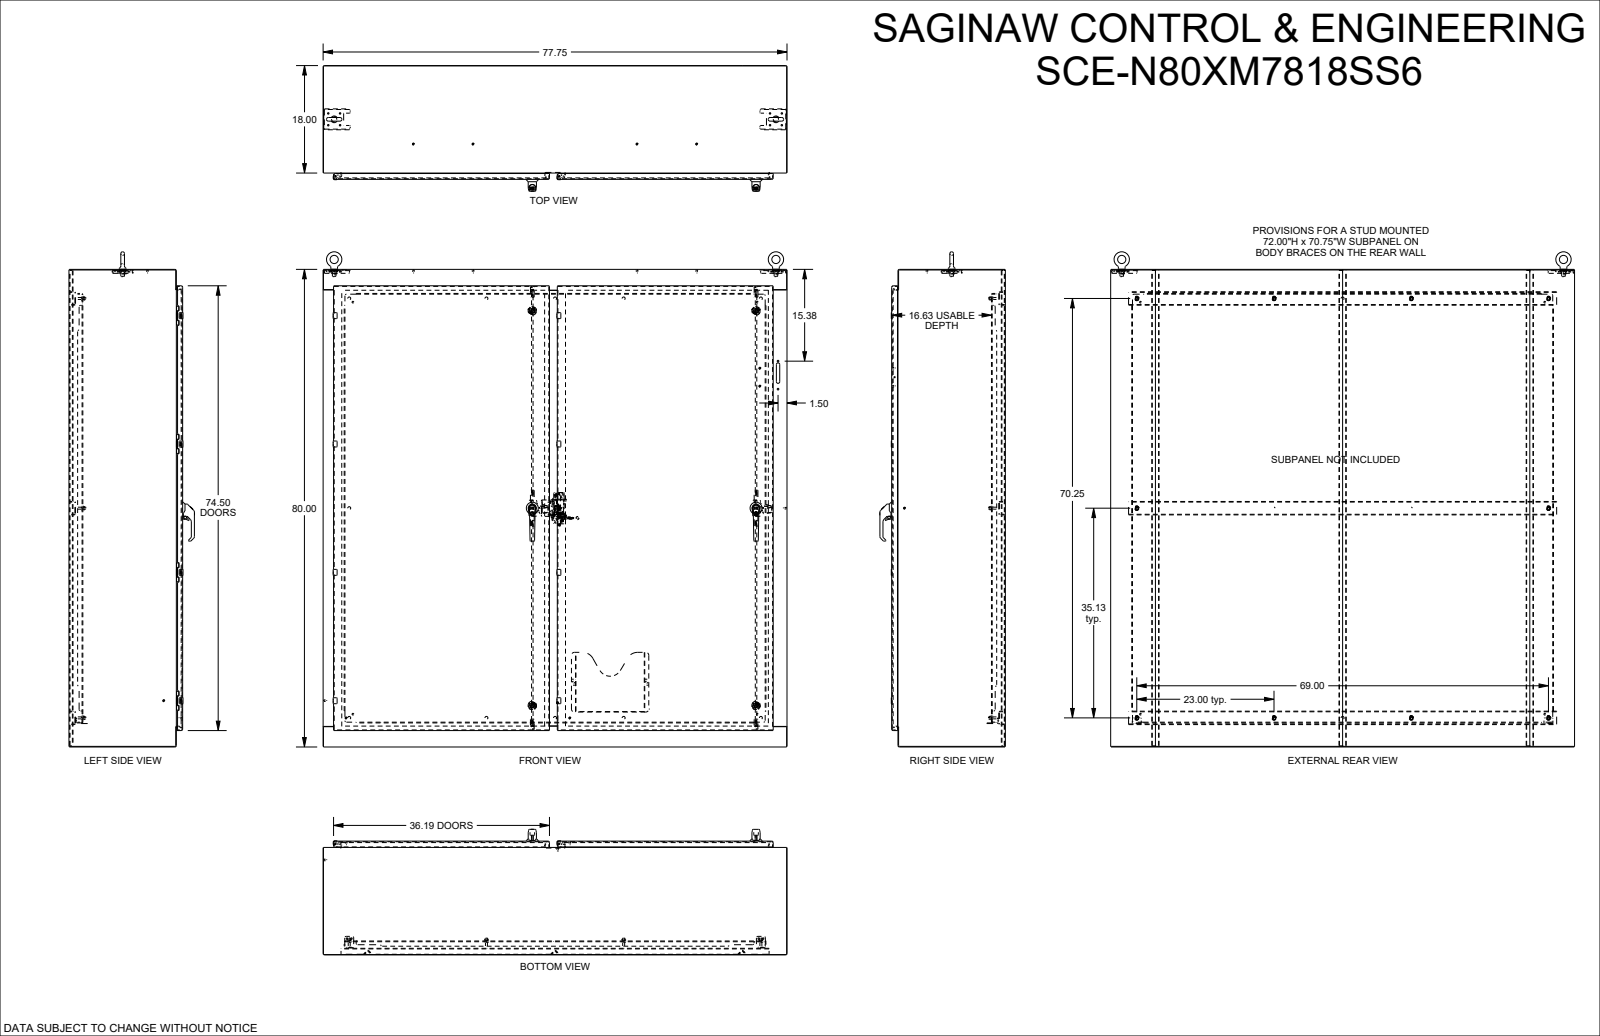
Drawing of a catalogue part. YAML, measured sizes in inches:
part_name: "SCE-N80XM7818"
step_written_by: "SolidWorks 2023 (AUTOMOTIVE_DESIGN)"
units: inches
bodies: {solids: 47, faces: 7363, planar: 3068, cylindrical: 2475, other: 1820}
overall_size: [82.945, 77.75, 21.046]
volume: 2246
surface_area: 42799
round_holes:
  - {diameter: 0.205, count: 16}
  - {diameter: 0.244, count: 16}
  - {diameter: 0.25, count: 14}
  - {diameter: 0.04, count: 8}
  - {diameter: 0.17, count: 8}
  - {diameter: 0.218, count: 8}
  - {diameter: 0.375, count: 8}
  - {diameter: 0.375, count: 8}
  - {diameter: 0.115, count: 4}
  - {diameter: 0.2, count: 4}
  - {diameter: 0.256, count: 4}
  - {diameter: 0.343, count: 4}
round_bosses_or_shafts:
  - {diameter: 0.17, count: 24}
  - {diameter: 0.25, count: 19}
  - {diameter: 0.24, count: 16}
  - {diameter: 0.196, count: 10}
  - {diameter: 1.4, count: 4}
  - {diameter: 0.341, count: 4}
  - {diameter: 2.008, count: 2}
  - {diameter: 1.173, count: 2}
partial_cylinders:
  - {radius: 0.03, count: 208}
  - {radius: 0.015, count: 162}
  - {radius: 0.125, count: 66}
  - {radius: 0.02, count: 65}
  - {radius: 0.04, count: 57}
  - {radius: 0.02, count: 48}
  - {radius: 0.25, count: 43}
  - {radius: 0.039, count: 42}
face_to_face_distances: [0.104, 18.954, 18.85, 19.058, 17.896, 1.058, 77.646, 79.896, 17.792, 1.162]
hole_center_spacings: [21.5, 43, 34.137, 37.5, 0.984, 1.399, 1.4, 1.548]
